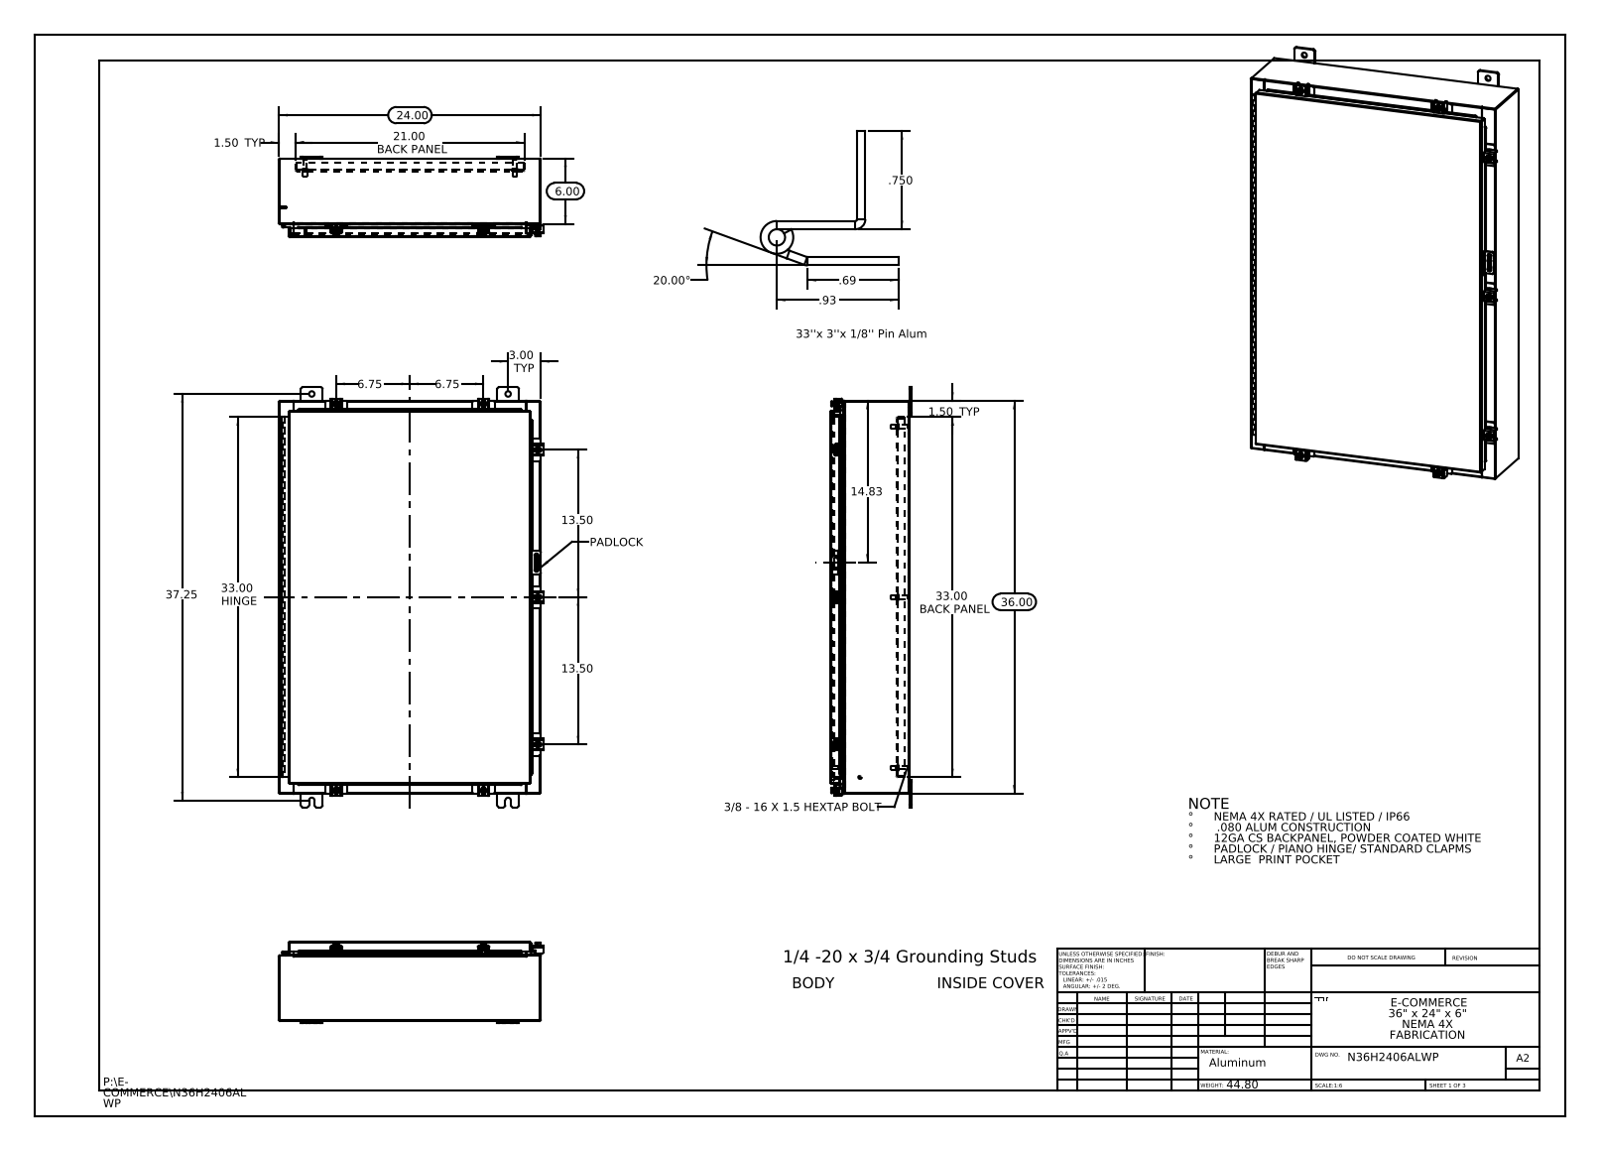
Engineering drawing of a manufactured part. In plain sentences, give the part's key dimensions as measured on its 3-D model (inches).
The part is named "N36H2406ALWP 22104005_DEFAULT; N36H2406ALWP Clamp Assembly; N36H2406ALWP Cover; N36H2406ALWP 22101002 (+8 more)". Its 3-D file was written by "SolidWorks 2013 (CONFIG_CONTROL_DESIGN)". It is 56 solids with 2210 faces: 1144 planar, 930 cylindrical and 136 other. Overall it measures 38.5 by 24.211 by 7.389 inches. Its volume is 292.8 cubic inches and its surface area 7 269 square inches. Round holes: 10 of diameter 0.5, 7 of diameter 0.213, 7 of diameter 0.26, 2 of diameter 0.125, 1 of diameter 0.125. Round bosses or shafts: 8 of diameter 0.25, 7 of diameter 0.5, 7 of diameter 0.399, 6 of diameter 0.625, 6 of diameter 0.375, 6 of diameter 0.33, 2 of diameter 0.315, 2 of diameter 0.236. Partial cylindrical surfaces (rounded edges, fillets, slot ends): 34 of radius 0.06, 27 of radius 0.013, 24 of radius 0.19, 21 of radius 0.088, 14 of radius 0.12, 14 of radius 0.141, 11 of radius 0.05, 10 of radius 0.08. The main face-to-face distances are 0.075, 7.126, 7.051, 7.201, 0.104, 1, 1.075, 6.051, 6.126, 1.179. The hole center spacings are 13.5, 15.625, 17.957, 24.793, 33.474, 37.154, 19.25, 1.858.
